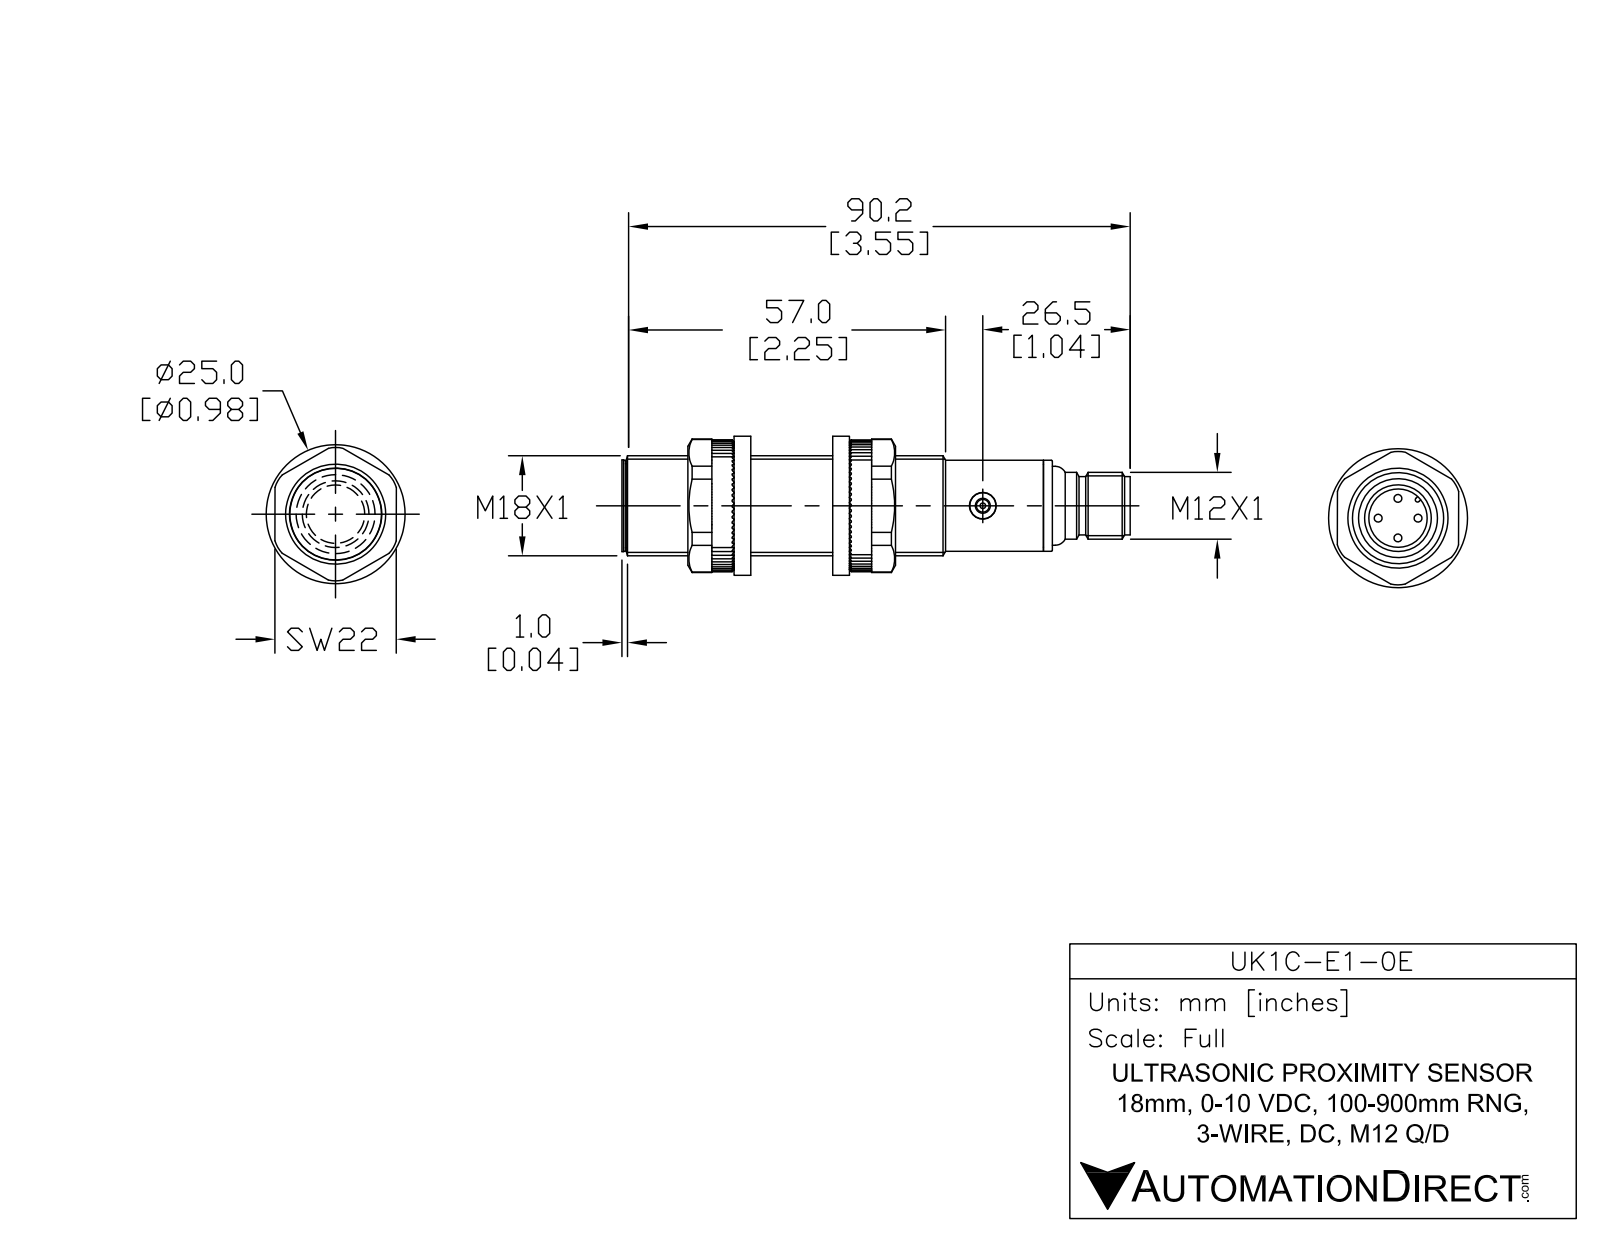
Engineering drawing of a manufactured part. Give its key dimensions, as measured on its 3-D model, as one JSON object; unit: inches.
{"part_name": "UK1C-E1-0E", "step_written_by": "SolidWorks 2017 (AUTOMOTIVE_DESIGN)", "units": "inches", "bodies": {"solids": 6, "faces": 106, "planar": 21, "cylindrical": 48, "other": 37}, "overall_size": [3.606, 0.709, 0.709], "volume_in3": 1.202, "surface_area_in2": 10.68, "round_holes": [[0.106, 1], [0.185, 1], [0.276, 1], [0.327, 1], [0.374, 1]], "round_bosses_or_shafts": [[0.039, 4], [0.709, 1], [0.654, 1], [0.646, 1], [0.622, 1], [0.559, 1], [0.472, 1], [0.413, 1]], "partial_cylinders_radius": [[0.024, 1]], "face_to_face_distances": [2.957, 0.039, 2.996, 0.037, 2.994, 0.043, 0.157, 3.055, 3.053, 3.016]}
